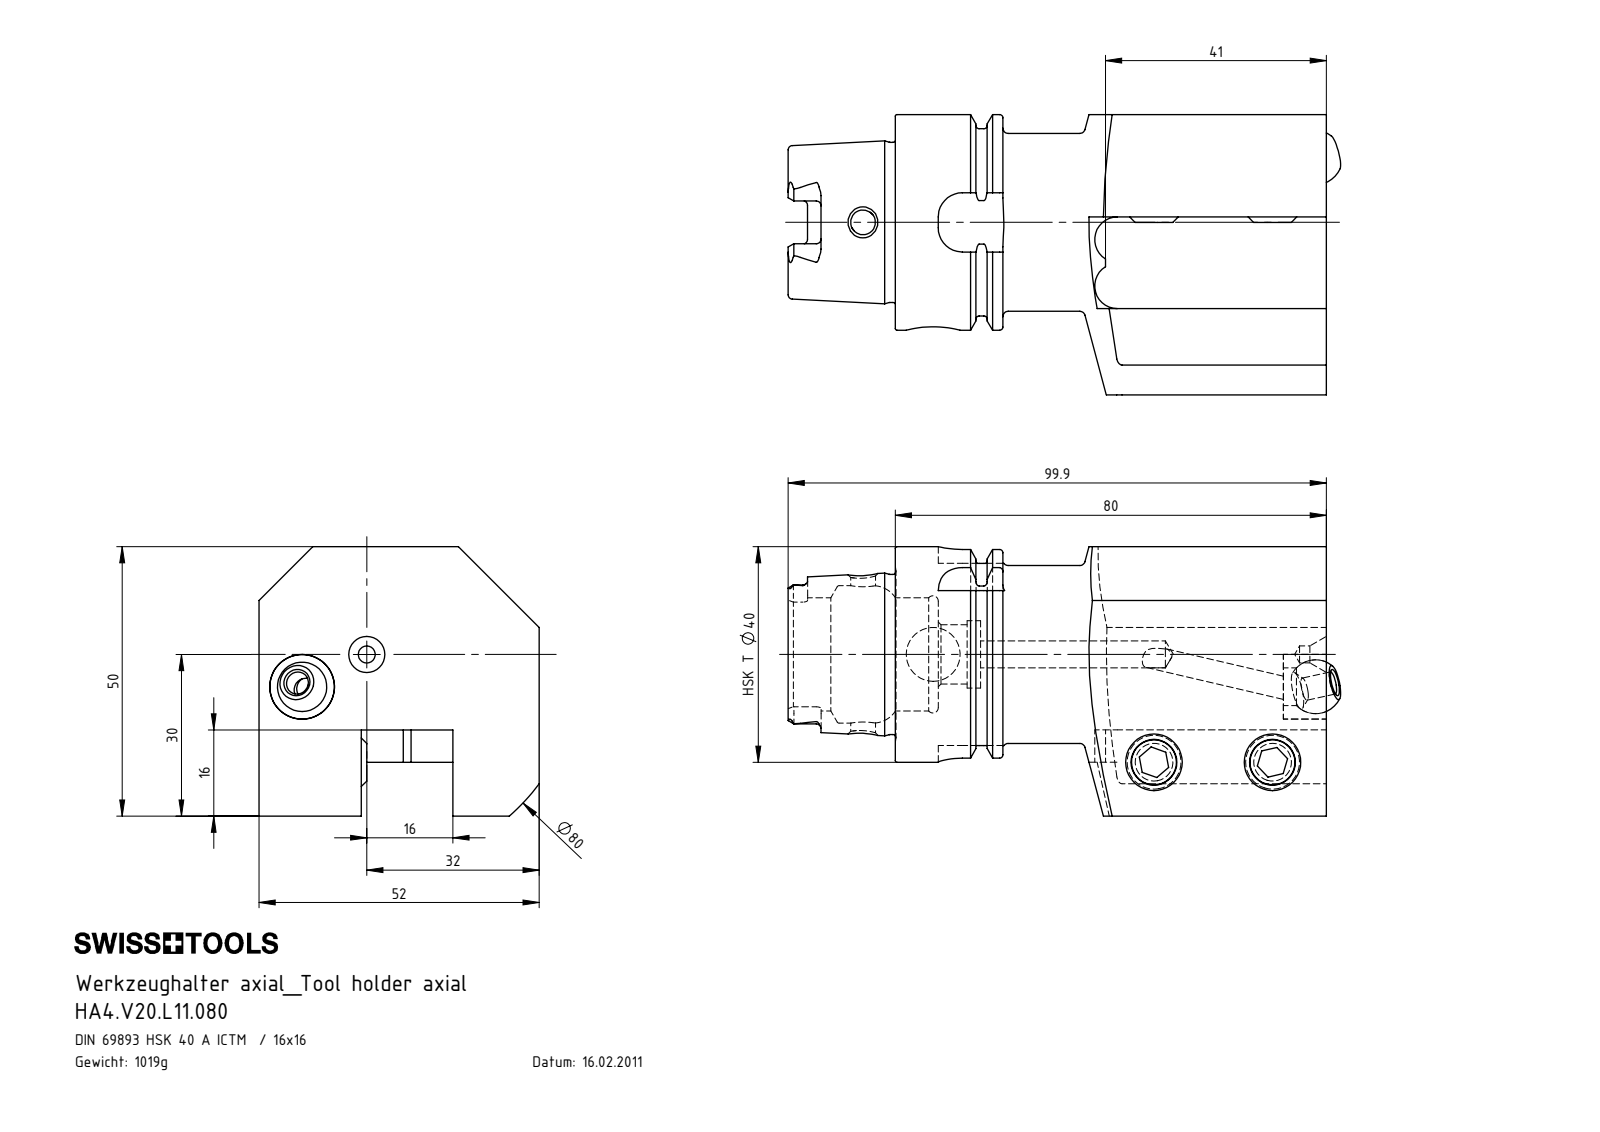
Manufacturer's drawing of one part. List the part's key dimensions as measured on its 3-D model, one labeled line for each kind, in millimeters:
Part name (STEP PRODUCT): HA4.V20.L11.080; ISO 4026 - M10 x 18; KU1-U12.001.010_1; HA4-V20.L11.080_A_Fertigbearbeitung (+2 more)
STEP written by: SolidWorks 2017 (AUTOMOTIVE_DESIGN)
Units: millimetres
Bodies: 5 solids, 247 faces (79 planar, 69 cylindrical, 99 other)
Overall size (bounding box): 101.7 × 52 × 50
Volume: 123 296 mm³ · Surface area: 27 587 mm²
Round holes (diameter × count): ⌀4.2 ×2, ⌀8.5 ×2, ⌀3.15 ×1, ⌀4.6 ×1, ⌀5 ×1, ⌀7 ×1, ⌀10 ×1, ⌀11 ×1, ⌀12 ×1, ⌀12.5 ×1, ⌀21 ×1, ⌀25.5 ×1
Round bosses / shafts (diameter × count): ⌀10 ×2, ⌀40 ×1, ⌀34.75 ×1, ⌀33 ×1, ⌀29.71 ×1
Partial cylindrical surfaces — rounded edges, fillets, slot ends (radius × count): R0.9 ×6, R1.88 ×4, R4.5 ×4, R4.7 ×2, R40 ×1
Main face-to-face distances: 52, 20, 50, 12, 30, 40, 33, 21, 19, 80
Hole centre spacings: 13.42, 22, 45.62, 66.1
